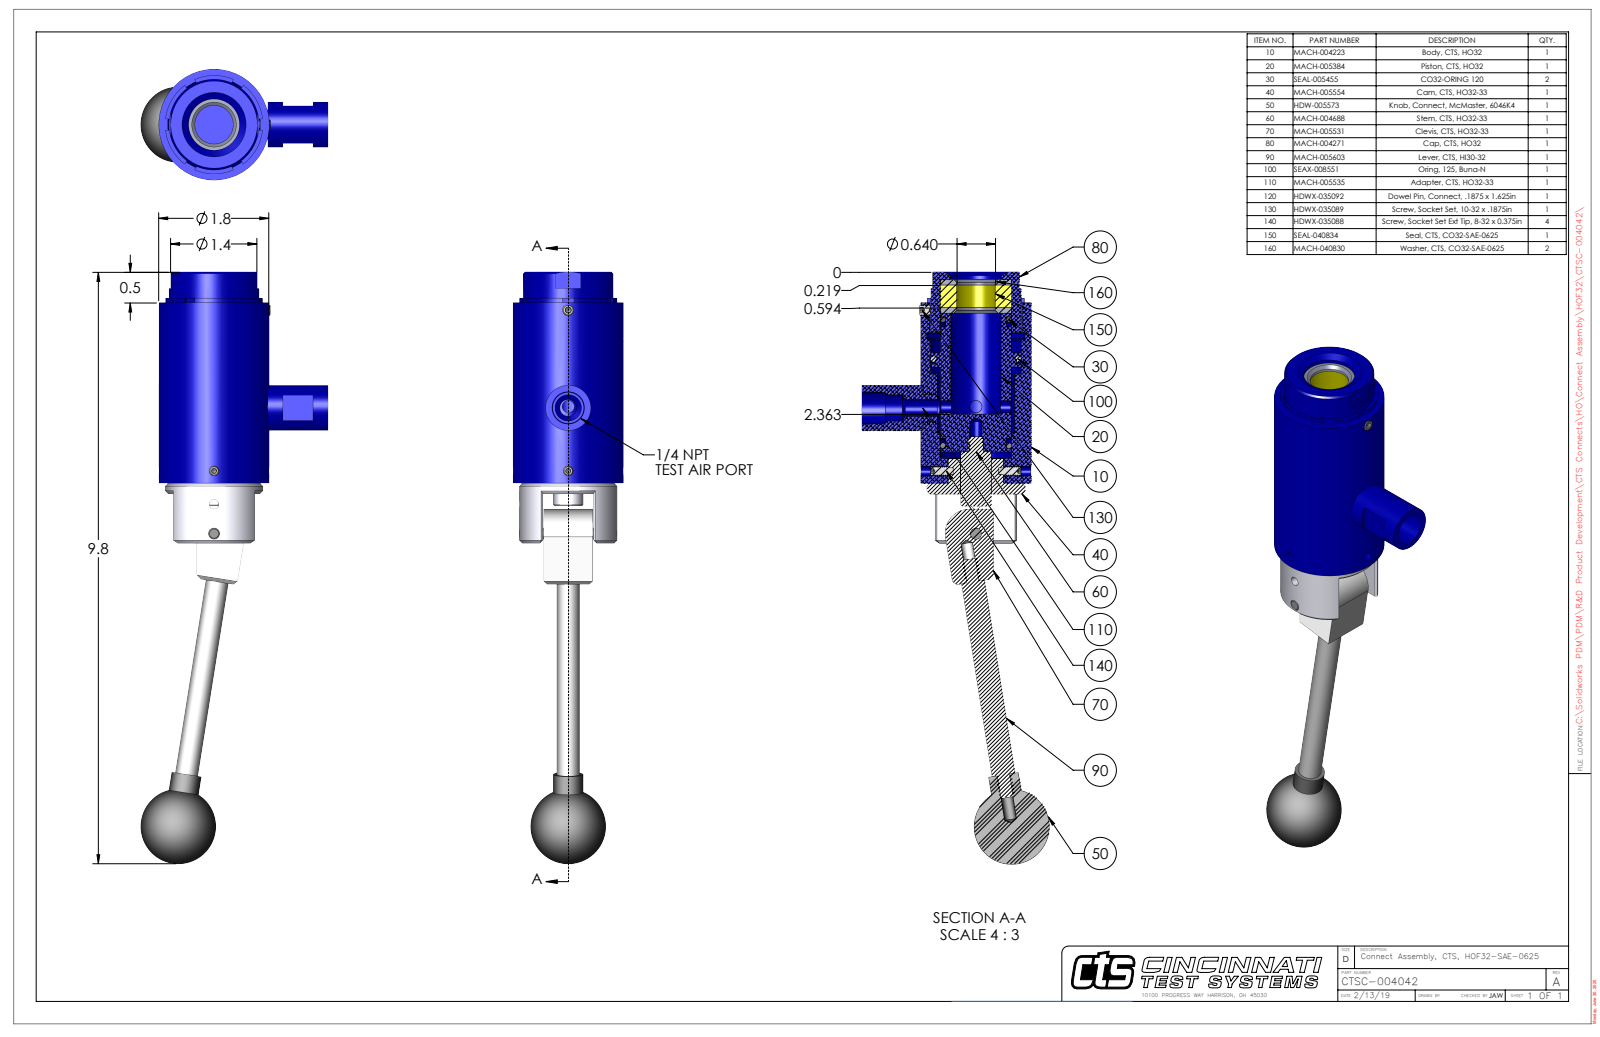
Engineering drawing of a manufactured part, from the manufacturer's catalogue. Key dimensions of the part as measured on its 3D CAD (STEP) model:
Part name (STEP PRODUCT): CTSC-004042
STEP written by: SolidWorks 2023 (AUTOMOTIVE_DESIGN)
Units: inches
Bodies: 14 solids, 530 faces (178 planar, 216 cylindrical, 136 other)
Overall size (bounding box): 9.837 × 3.109 × 1.832
Volume: 10.86 in³ · Surface area: 84.34 in²
Round holes (diameter × count): ⌀0.201 ×3, ⌀0.159 ×2, ⌀0.094 ×1, ⌀0.189 ×1, ⌀0.19 ×1, ⌀0.203 ×1, ⌀0.203 ×1, ⌀0.281 ×1, ⌀0.438 ×1, ⌀0.453 ×1, ⌀0.516 ×1, ⌀0.53 ×1
Round bosses / shafts (diameter × count): ⌀0.75 ×2, ⌀0.5 ×2, ⌀0.164 ×2, ⌀0.109 ×2, ⌀1.832 ×1, ⌀1.625 ×1, ⌀1.495 ×1, ⌀1.172 ×1
Partial cylindrical surfaces — rounded edges, fillets, slot ends (radius × count): R0.228 ×1, R0.4 ×1, R0.77 ×1, R0.811 ×1, R0.846 ×1
Main face-to-face distances: 0.014, 0.826, 0.178, 3, 0.375, 2.916, 3.291, 3.385, 0.469, 0.094
Hole centre spacings: 0.022, 0.488, 1.128, 1.603, 1.622, 1.625, 2.11, 2.75
